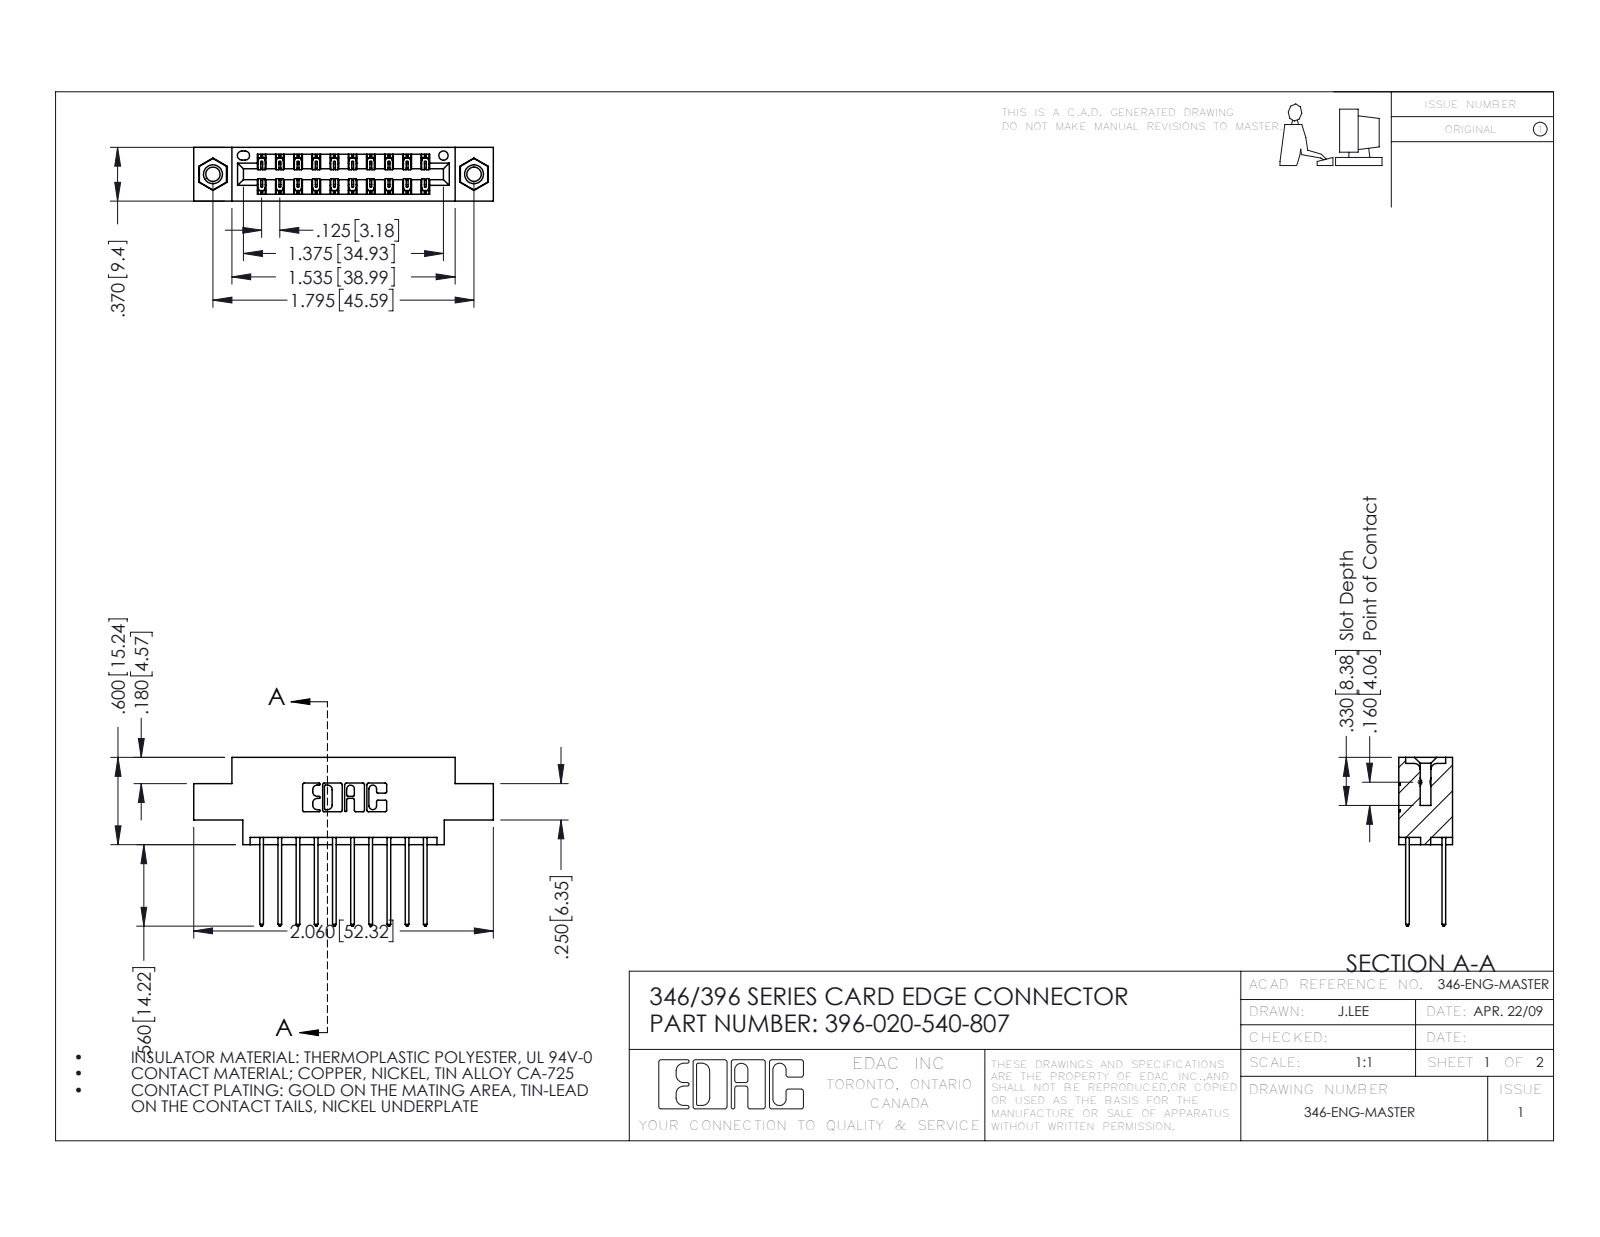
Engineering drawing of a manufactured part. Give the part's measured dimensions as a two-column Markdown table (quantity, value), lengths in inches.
| quantity | value |
| --- | --- |
| part name | 345-250-001_345-250-005-103; 345-292-001_345-293-140; 396-020-540-807; 346 Part_0.170 Offset - 0.156 Dia-TI |
| STEP written by | SolidWorks 2016 (CONFIG_CONTROL_DESIGN) |
| units | inches |
| bodies | 23 solids, 1226 faces (812 planar, 398 cylindrical, 16 other) |
| overall size | 2.06 × 1.16 × 0.37 |
| volume | 0.291 in³ |
| surface area | 10.25 in² |
| round holes (diameter × count) | 0.098 × 2, 0.125 × 2, 0.156 × 2, 0.064 × 1 |
| round bosses / shafts (diameter × count) | 0.155 × 2 |
| partial cylindrical surfaces (radius × count) | 0.006 × 30, 0.01 × 22, 0.01 × 20, 0.007 × 6, 0.031 × 6, 0.026 × 3, 0.014 × 2, 0.022 × 2 |
| main face-to-face distances | 0.25, 0.048, 0.322, 0.37, 0.072, 0.298, 0.025, 0.275, 0.222, 0.148 |
| hole center spacings | 0.246, 1.59, 1.795 |
